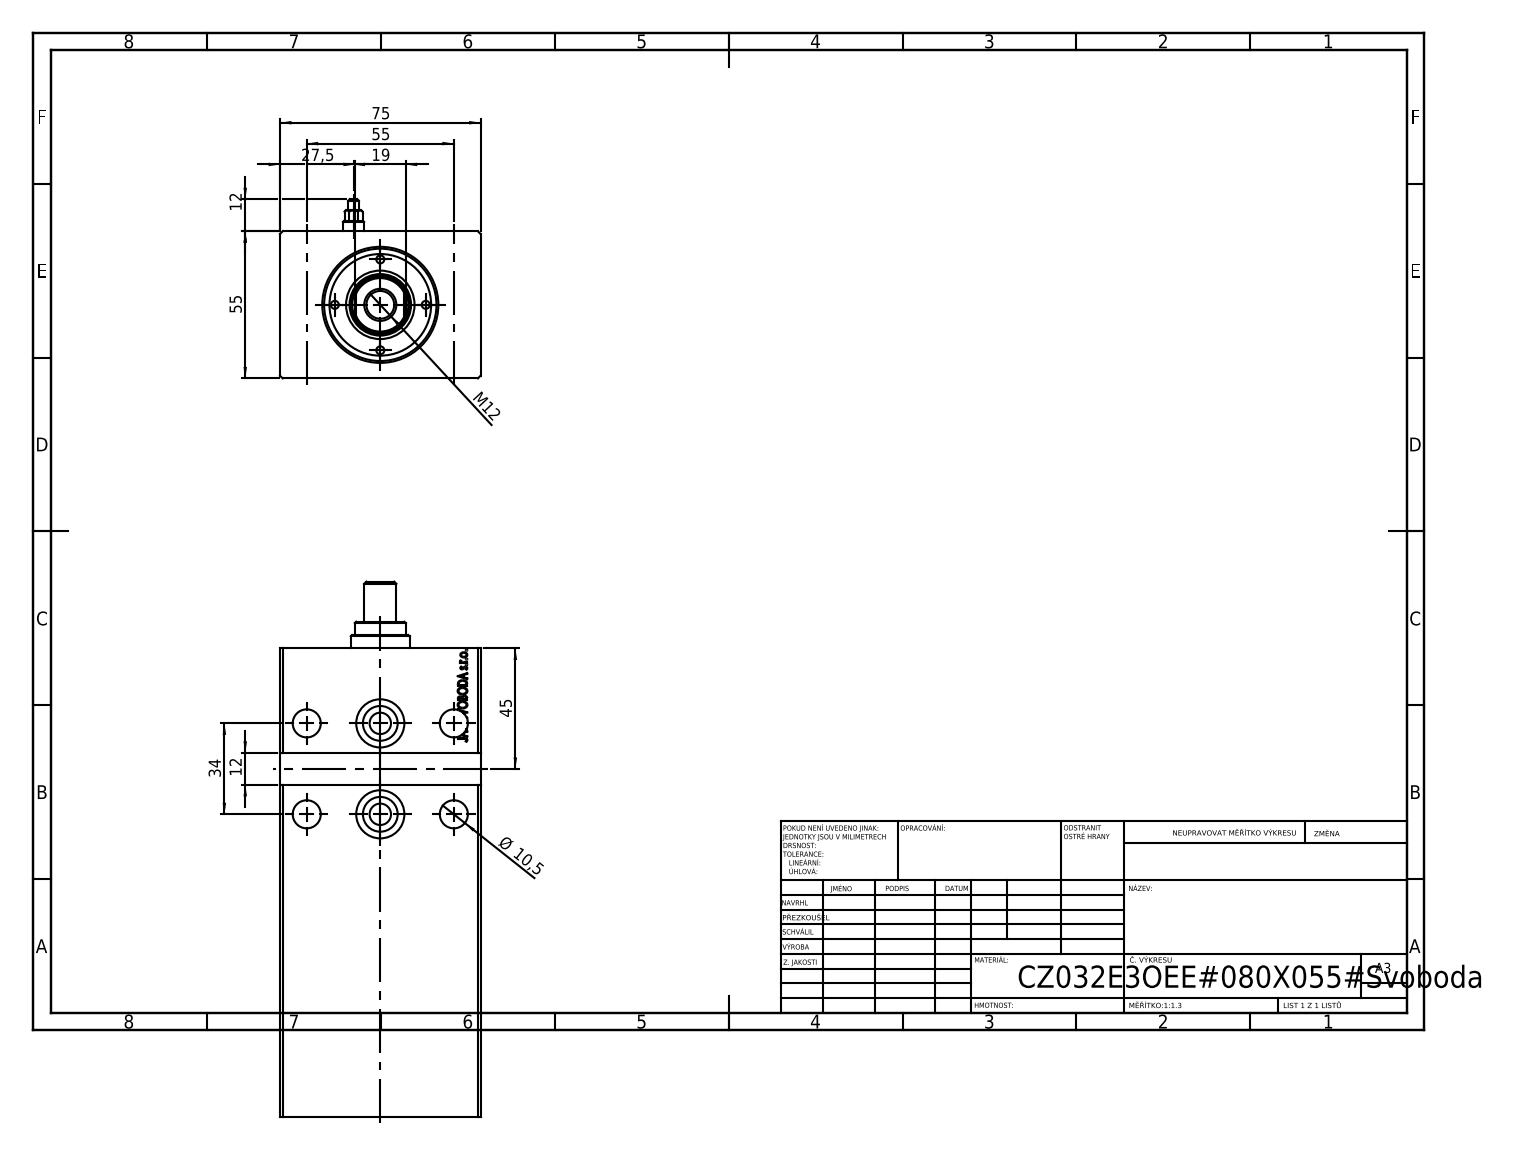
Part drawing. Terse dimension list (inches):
name: Zatka_Cushioning3; V500CZ_B_VC; V500CZ_SMALL_MALE_METRIC; V500CZ_E (+1 more)
written by: SolidWorks 2019 (CONFIG_CONTROL_DESIGN)
unit: in
bodies: 6 solids, 876 faces (412 planar, 68 cylindrical, 396 other)
size: 7.874 × 2.953 × 2.638
volume: 40.78 in³; area: 154.1 in²
holes: 5× ⌀0.413, 4× ⌀0.118, 4× ⌀0.315, 2× ⌀0.071, 2× ⌀0.709, 1× ⌀0.866, 1× ⌀0.906, 1× ⌀1.26, 1× ⌀1.417, 1× ⌀1.654
bosses: 2× ⌀0.512, 2× ⌀0.307, 2× ⌀0.15, 1× ⌀1.496, 1× ⌀0.472
rounds: 1× R0.413
face distances: 2.165, 2.953, 6.89, 0.394, 6.346, 0.543, 5.953, 6.496, 6.882, 6.488
hole spacings: 1.339, 0.669, 0.946, 1.083, 1.722, 2.165, 2.546, 0.44
